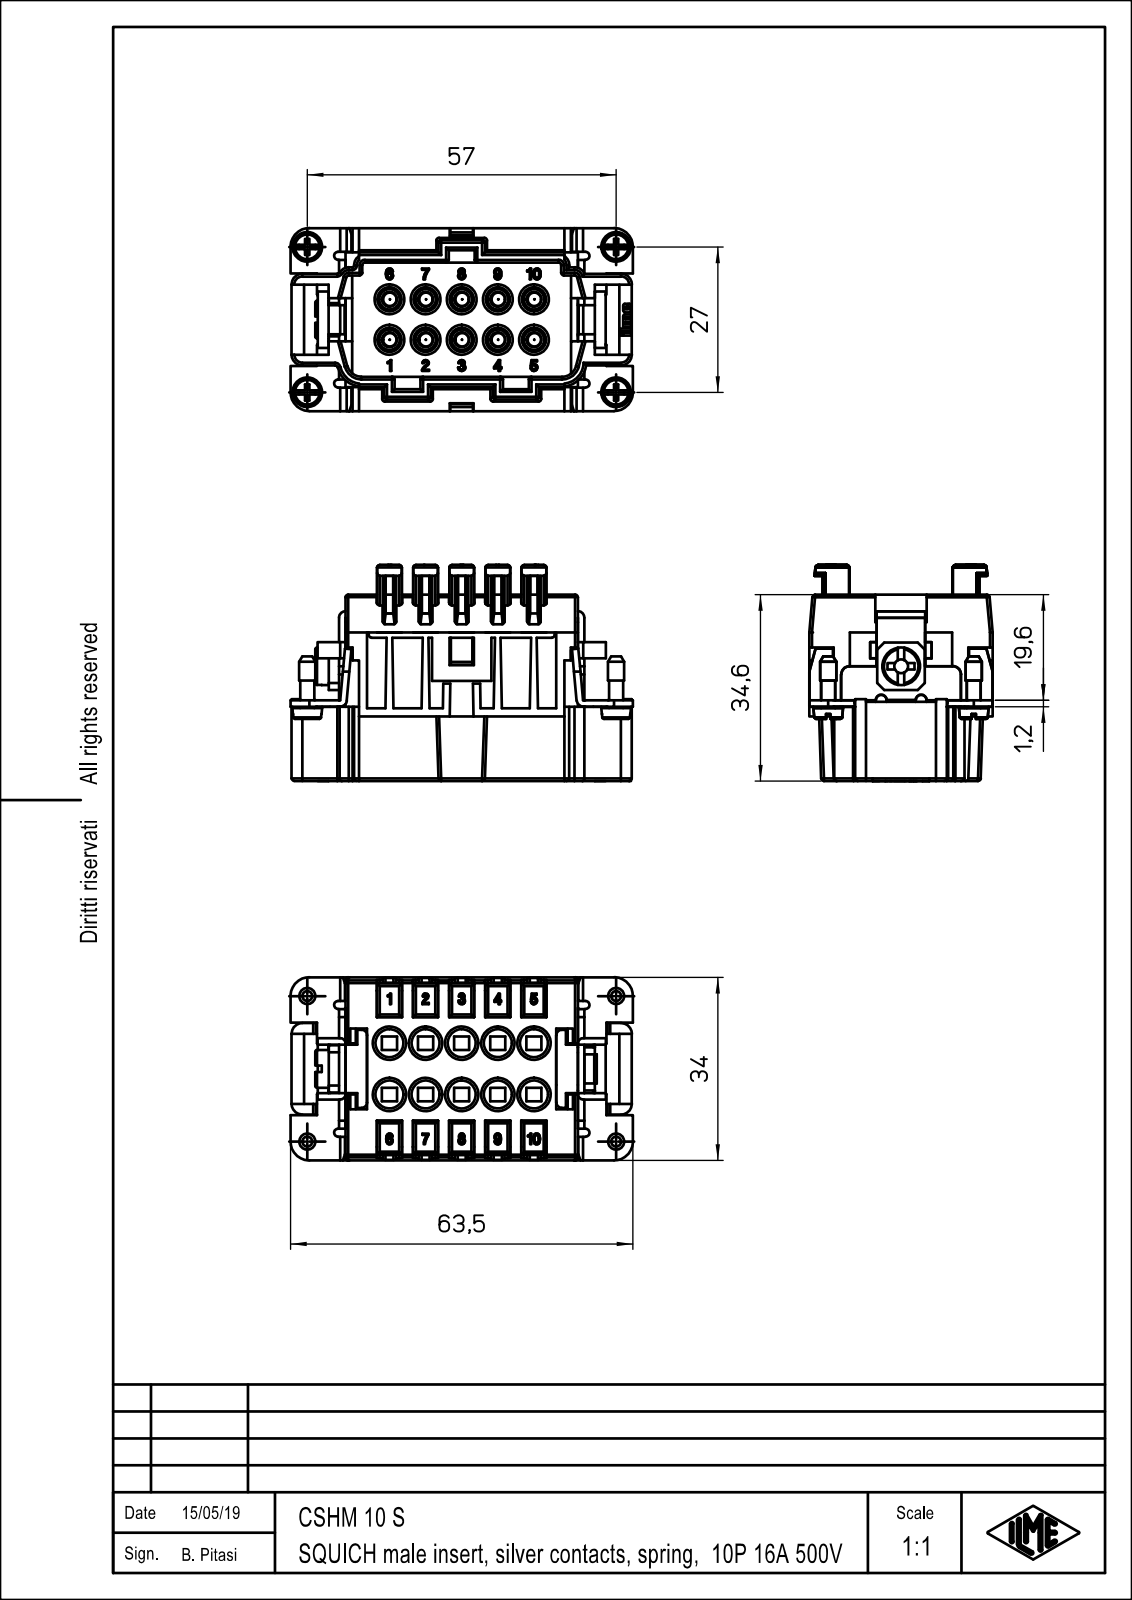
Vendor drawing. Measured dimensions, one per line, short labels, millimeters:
name: CSHM_10_S
written by: Creo Elements/Direct Modeling 20.1B 02-Apr-2019 (C) Parametric Technology GmbH (AUTOMOTIVE_DESIGN)
unit: mm
bodies: 1 solid, 1559 faces (943 planar, 427 cylindrical, 189 other)
size: 63.5 × 40.1 × 34
volume: 34 143 mm³; area: 23 290 mm²
holes: 10× ⌀5.2, 4× ⌀2.8, 1× ⌀2.58, 1× ⌀4.2
bosses: 10× ⌀2.5, 4× ⌀5.5, 4× ⌀3, 4× ⌀2.6, 1× ⌀7, 1× ⌀6, 1× ⌀4
rounds: 134× R0.5, 23× R0.3, 12× R1, 10× R1.15, 10× R2, 6× R1.2, 4× R0.75, 4× R3.5
face distances: 1.5, 20.1, 12.5, 4, 1.2, 26.1, 6.7, 14, 27.6, 4.9
hole spacings: 6.7, 11.62, 13.4, 16.43, 9.5, 17.58, 20.1, 22.23
